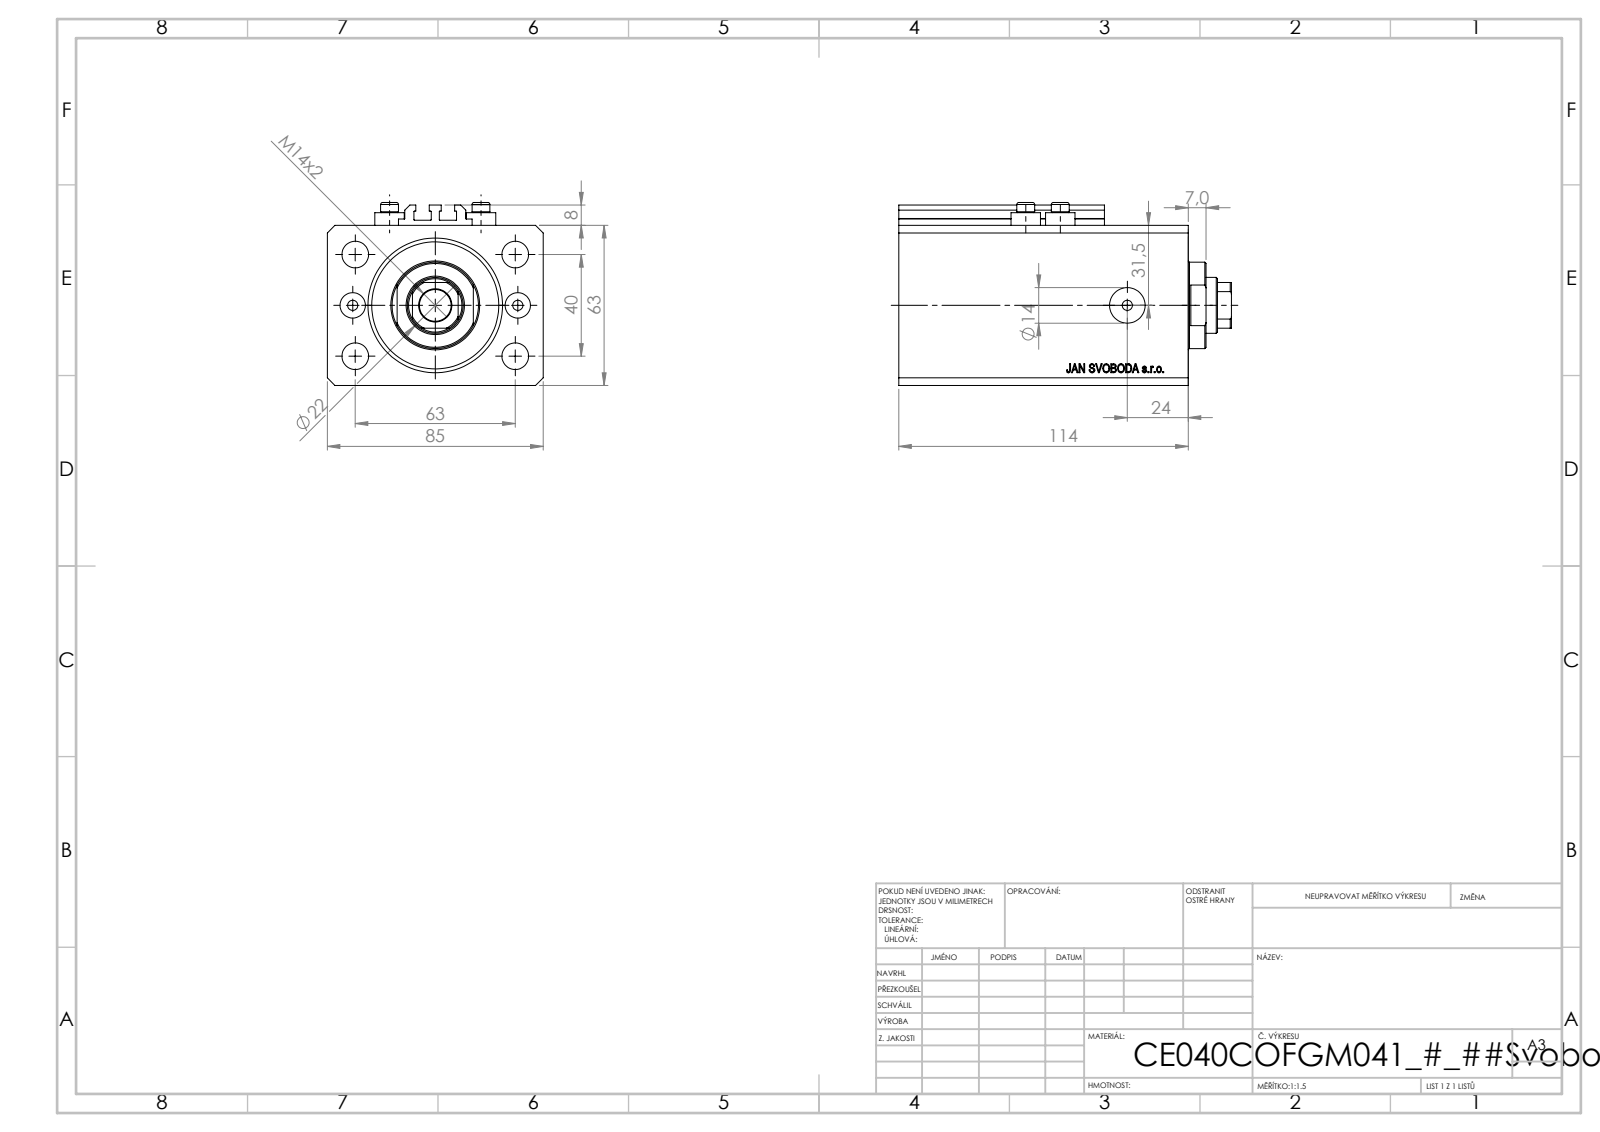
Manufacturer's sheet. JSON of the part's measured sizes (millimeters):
{"part_name": "V250CE_C_Body; V250CE_VC_C; ALLEN BOLT V250CE; V250CE_C_VCP", "step_written_by": "SolidWorks 2019 (CONFIG_CONTROL_DESIGN)", "units": "millimeters", "bodies": {"solids": 8, "faces": 1034, "planar": 504, "cylindrical": 86, "other": 444}, "overall_size": [131, 85, 72], "volume_mm3": 549181, "surface_area_mm2": 107239, "round_holes": [[4, 8], [10.5, 4], [10, 2], [14, 2], [12.5, 1], [22, 1], [40, 1], [53, 1]], "round_bosses_or_shafts": [[11.6, 4], [7, 4], [34, 1]], "partial_cylinders_radius": [[0.2, 10], [10.5, 1]], "face_to_face_distances": [63, 85, 114, 17, 97, 11.4, 85.6, 102.6, 65, 3], "hole_center_spacings": [20.02, 37.31, 67.05, 13.6, 32.5, 36, 38.48, 40]}
